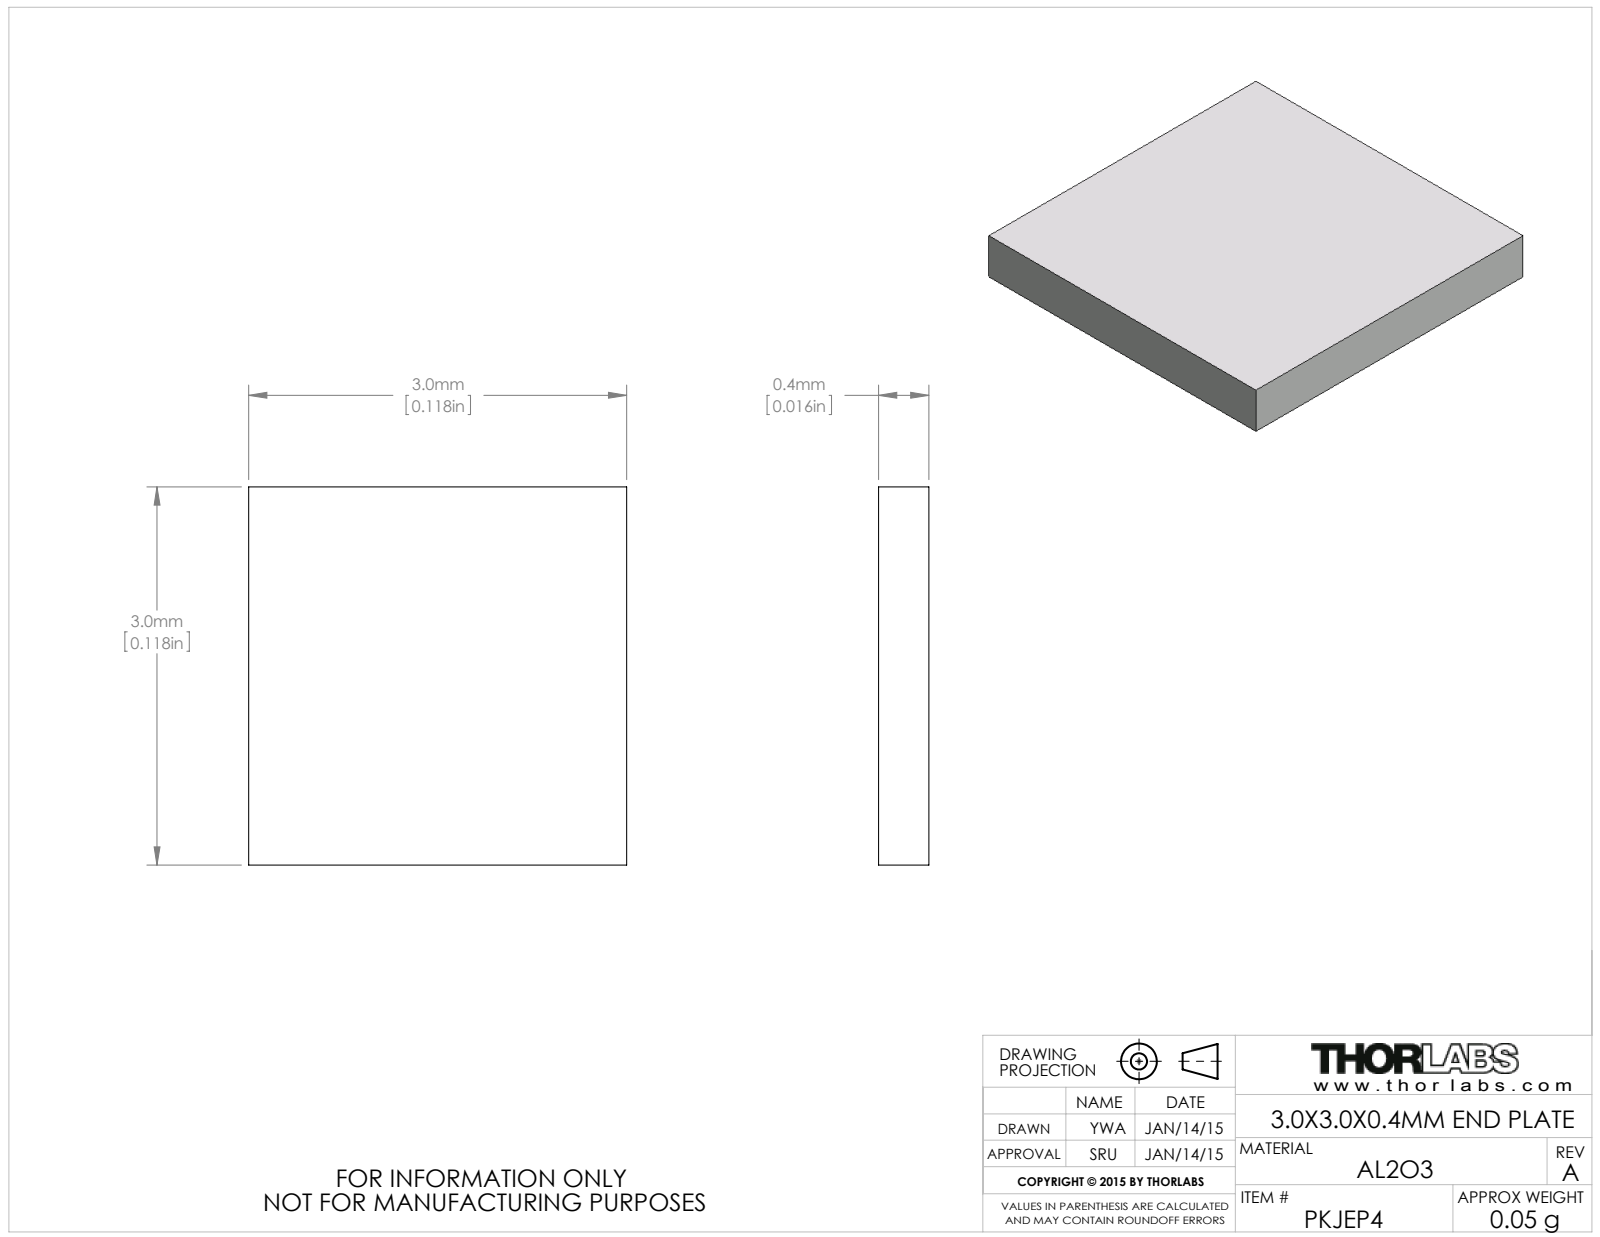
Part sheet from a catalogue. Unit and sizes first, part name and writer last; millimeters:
Units: millimetres
Overall size (bounding box): 3 × 3 × 0.4
Main face-to-face distances: 0.4, 3
Volume: 4 mm³ · Surface area: 23 mm²
Bodies: 1 solid, 6 faces (6 planar, 0 cylindrical, 0 other)
Part name (STEP PRODUCT): PKJEP4
STEP written by: SolidWorks 2012 (AUTOMOTIVE_DESIGN)
